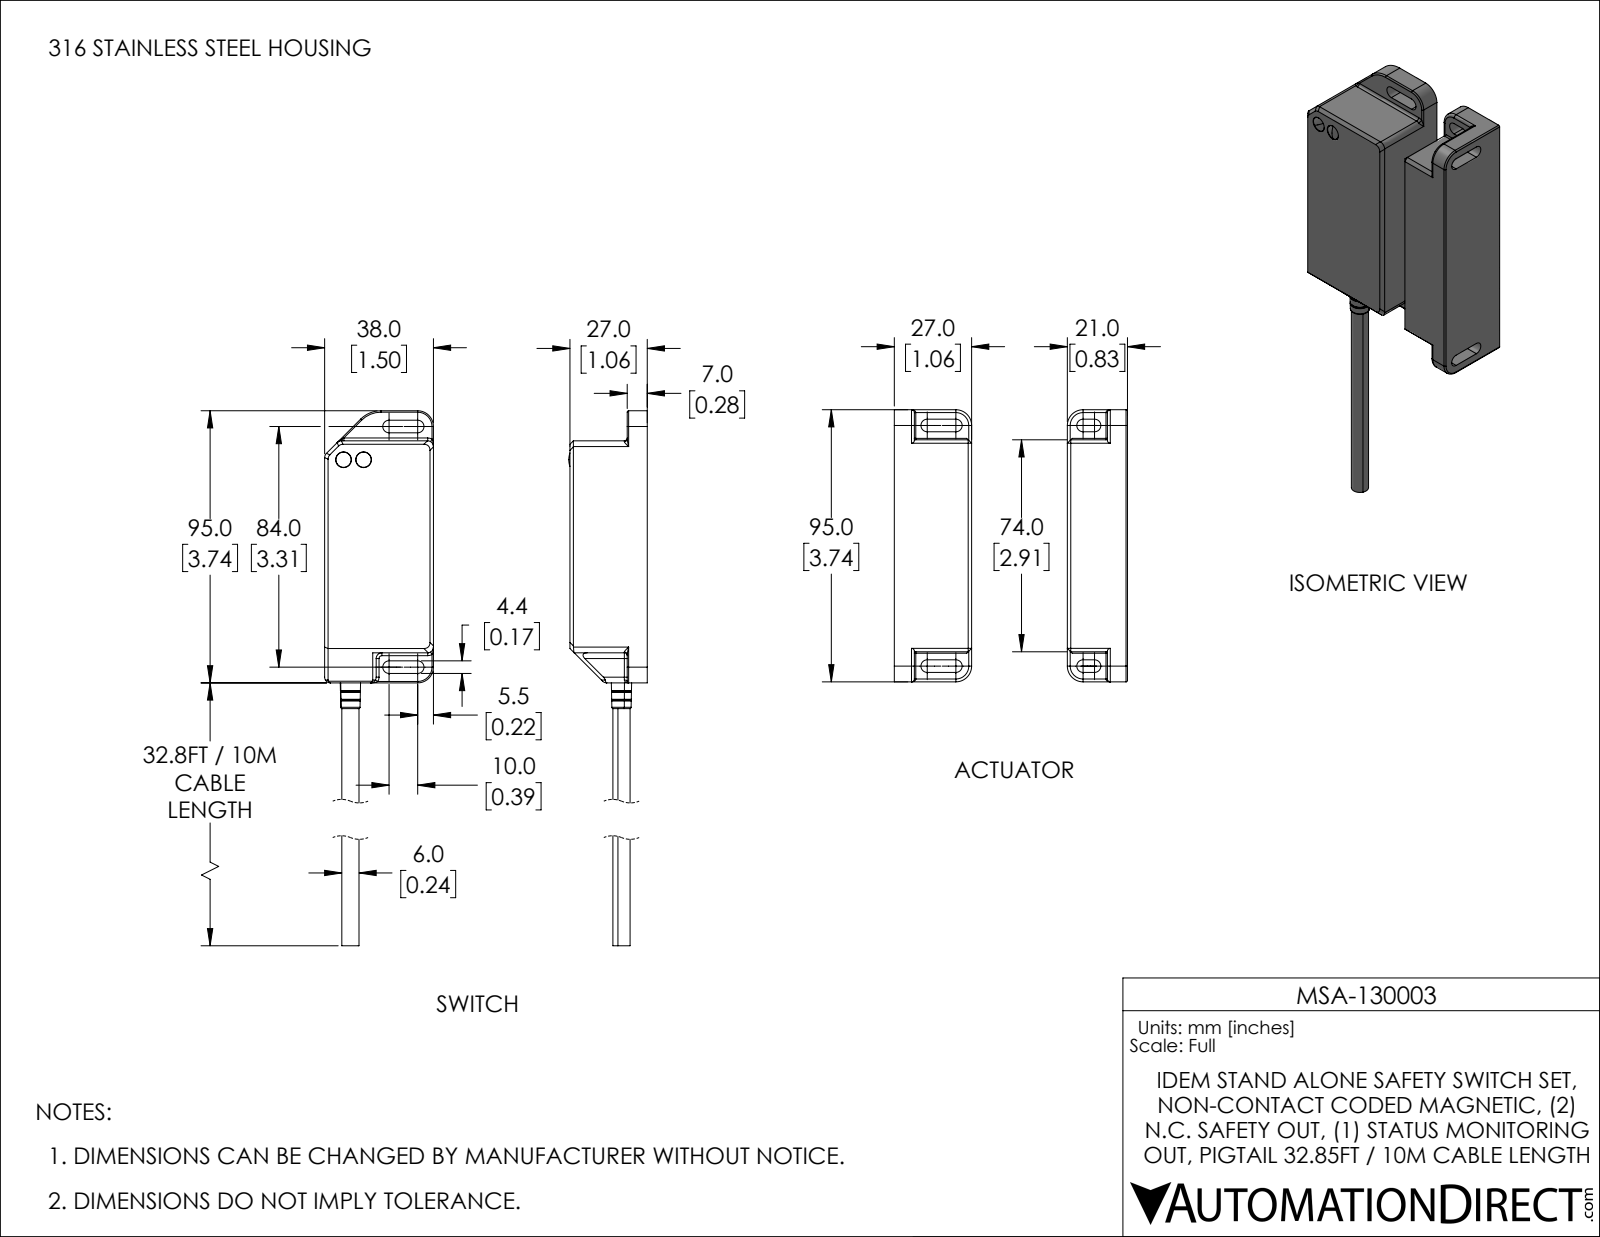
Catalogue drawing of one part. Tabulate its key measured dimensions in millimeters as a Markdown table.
| quantity | value |
| --- | --- |
| part name | MSA-130002 |
| STEP written by | SolidWorks 2019 (AUTOMOTIVE_DESIGN) |
| units | millimeters |
| bodies | 2 solids, 925 faces (431 planar, 238 cylindrical, 256 other) |
| overall size | 180.1 × 69 × 27.4 |
| volume | 47 930 mm³ |
| surface area | 43 480 mm² |
| round holes (diameter × count) | 2.9 × 2, 5.5 × 2, 8.2 × 1 |
| round bosses / shafts (diameter × count) | 5.3 × 2, 5 × 2, 4.5 × 2, 2 × 2, 8.6 × 1, 7.6 × 1, 7.1 × 1, 6 × 1 |
| partial cylindrical surfaces (radius × count) | 0.5 × 88, 2.2 × 12, 1 × 11, 2 × 10, 0.3 × 8, 5.5 × 6, 0.2 × 4, 3 × 4 |
| main face-to-face distances | 2, 26.8, 48, 31, 24.8, 25.2, 23.2, 1.6, 12, 19 |
| hole center spacings | 7 |
